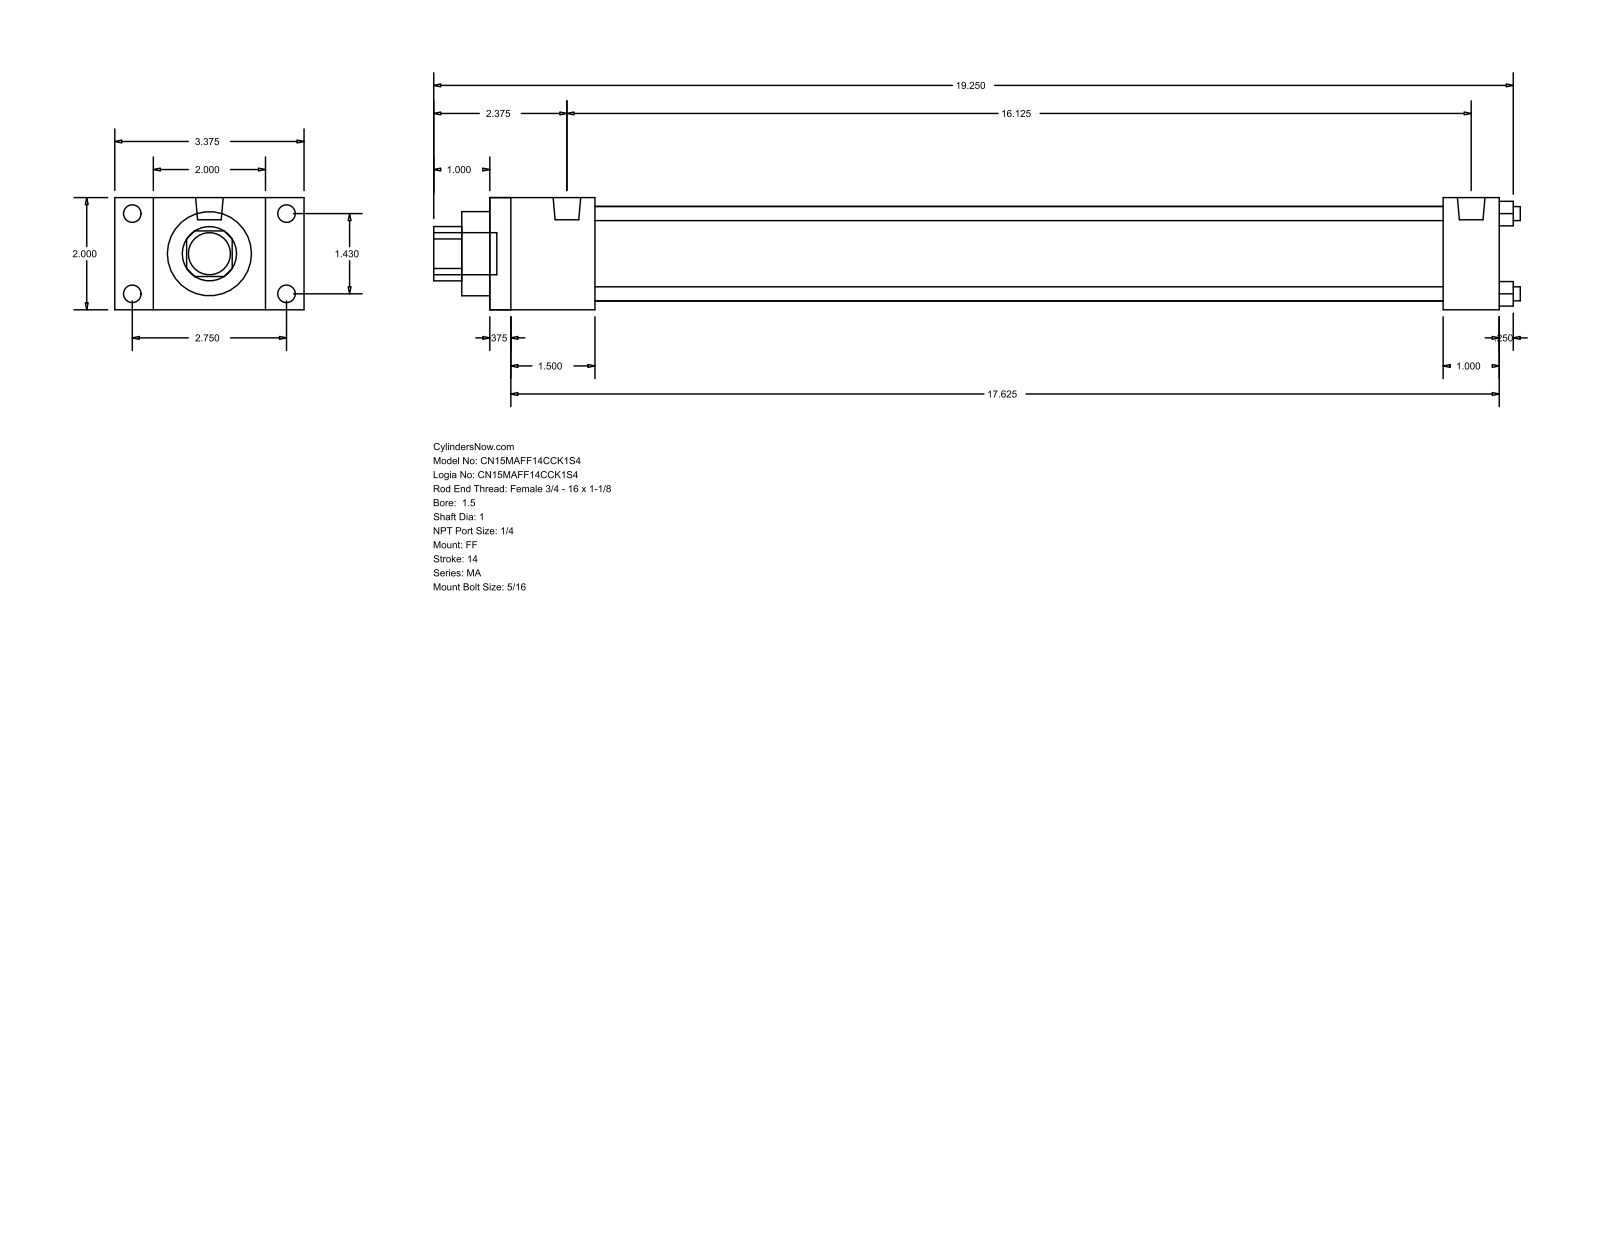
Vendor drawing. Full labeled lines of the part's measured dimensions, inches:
Part name (STEP PRODUCT): MA_FF__0150_1
STEP written by: GSSL Pune (CONFIG_CONTROL_DESIGN)
Units: inches
Bodies: 0 solids, 92 faces (64 planar, 28 cylindrical, 0 other)
Overall size (bounding box): 19.375 × 3.375 × 2
Round holes (diameter × count): ⌀0.25 ×4, ⌀1 ×1, ⌀1.5 ×1, ⌀1.69 ×1
Round bosses / shafts (diameter × count): ⌀0.313 ×8, ⌀0.492 ×2, ⌀0.75 ×1
Partial cylindrical surfaces — rounded edges, fillets, slot ends (radius × count): R0.484 ×1
Main face-to-face distances: 2, 18, 0.375, 17.625, 1, 1.875, 17, 1.5, 16.625, 15.125
Hole centre spacings: 1.011, 1.43, 2.022
